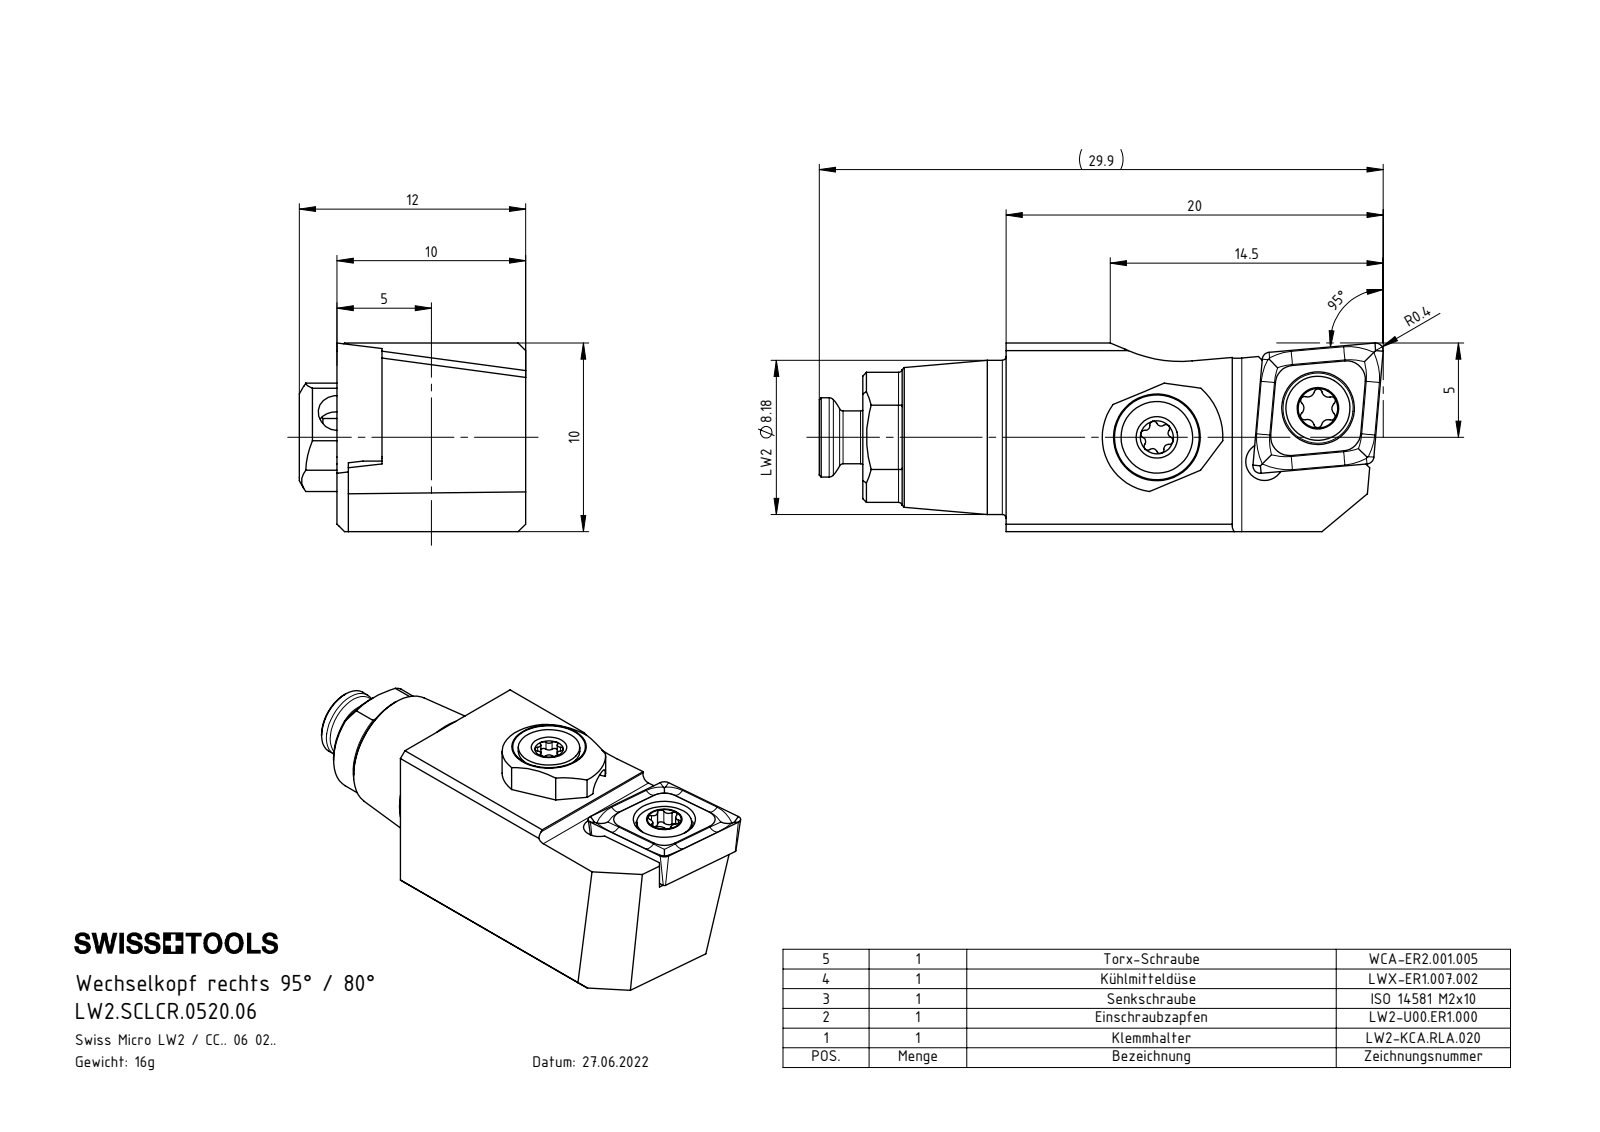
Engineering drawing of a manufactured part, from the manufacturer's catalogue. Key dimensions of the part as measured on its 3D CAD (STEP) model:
Part name (STEP PRODUCT): LWX-ER1.007.002; LW2-KCA.RLA.020_B; LW2.SCLCR.0520.06; ISO 14581 - M2x10 (+3 more)
STEP written by: SolidWorks 2017 (CONFIG_CONTROL_DESIGN)
Units: millimetres
Bodies: 6 solids, 190 faces (63 planar, 64 cylindrical, 63 other)
Overall size (bounding box): 29.9 × 12 × 10
Volume: 2 007 mm³ · Surface area: 1 779 mm²
Round holes (diameter × count): ⌀1 ×1, ⌀1.5 ×1, ⌀1.6 ×1, ⌀2 ×1, ⌀2.05 ×1, ⌀2.8 ×1, ⌀3 ×1, ⌀3.5 ×1, ⌀3.85 ×1
Round bosses / shafts (diameter × count): ⌀8.18 ×1, ⌀4.2 ×1, ⌀4 ×1, ⌀3.8 ×1, ⌀3.4 ×1, ⌀3 ×1, ⌀2.8 ×1, ⌀2.5 ×1
Partial cylindrical surfaces — rounded edges, fillets, slot ends (radius × count): R0.2 ×8, R0.19 ×6, R0.21 ×6, R0.24 ×6, R0.29 ×6, R0.36 ×5, R0.36 ×1, R0.5 ×1
Main face-to-face distances: 10, 7.62, 2.38, 9.4, 1.78, 0.6, 7.6, 1.1, 2, 8
Hole centre spacings: 4, 4.02, 5.85, 8.68, 8.69
